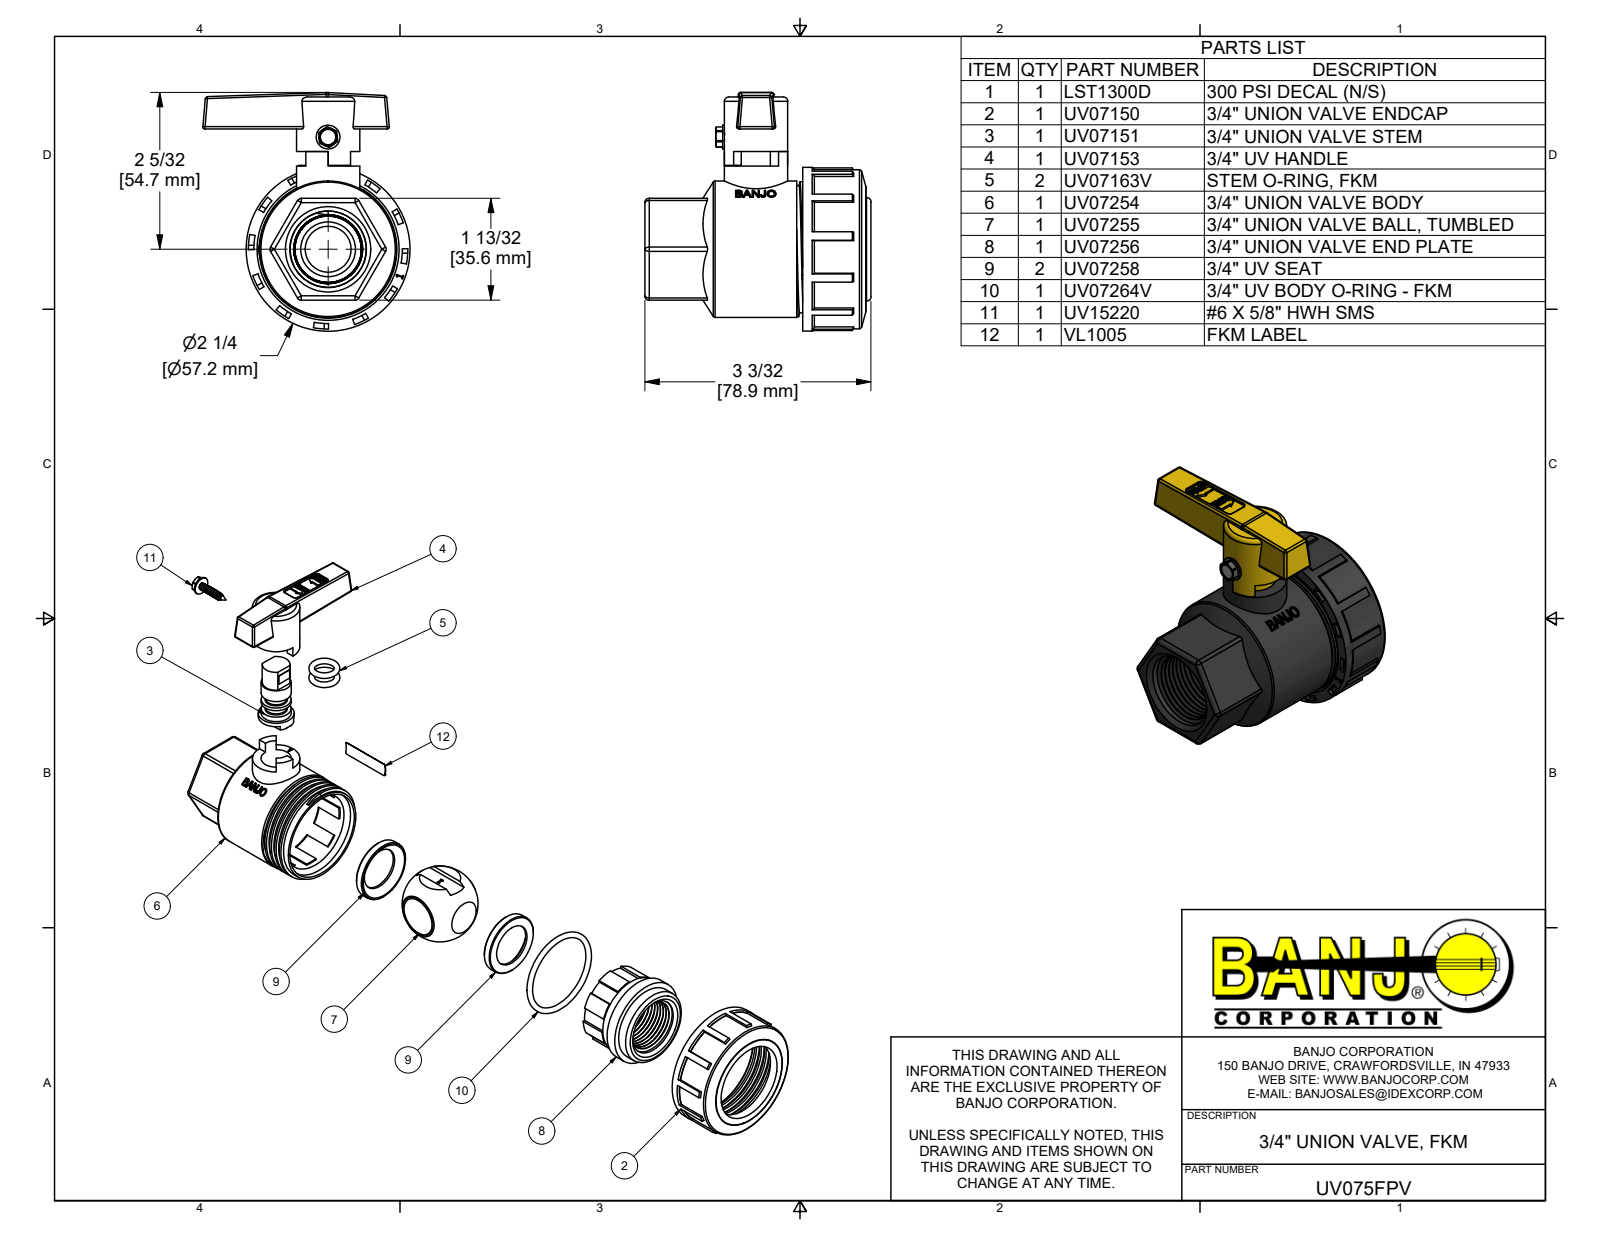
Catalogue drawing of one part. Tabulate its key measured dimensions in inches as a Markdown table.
| quantity | value |
| --- | --- |
| part name | UV075FPV; UV07254; UV07256; UV07150 (+8 more) |
| STEP written by | Autodesk Inventor 2019 (AUTOMOTIVE_DESIGN) |
| units | inches |
| bodies | 13 solids, 959 faces (456 planar, 202 cylindrical, 301 other) |
| overall size | 30.801 × 3.279 × 2.848 |
| volume | 6.802 in³ |
| surface area | 250 in² |
| round holes (diameter × count) | 0.515 × 1, 0.558 × 1, 0.727 × 1, 0.75 × 1, 0.76 × 1, 0.79 × 1, 1.153 × 1, 1.157 × 1, 1.45 × 1, 1.5 × 1, 1.67 × 1, 1.778 × 1 |
| round bosses / shafts (diameter × count) | 2.25 × 1, 2.187 × 1, 1.875 × 1, 1.856 × 1, 1.75 × 1, 1.625 × 1, 1.47 × 1, 1.42 × 1 |
| partial cylindrical surfaces (radius × count) | 0.03 × 26, 0.06 × 12, 0.01 × 4, 0.05 × 4, 0.5 × 3, 0.139 × 1, 0.255 × 1, 0.287 × 1 |
| main face-to-face distances | 1.4, 1.951, 1.22, 0.731, 0.7, 0.11, 0.031, 1.251, 0.115, 1.285 |
